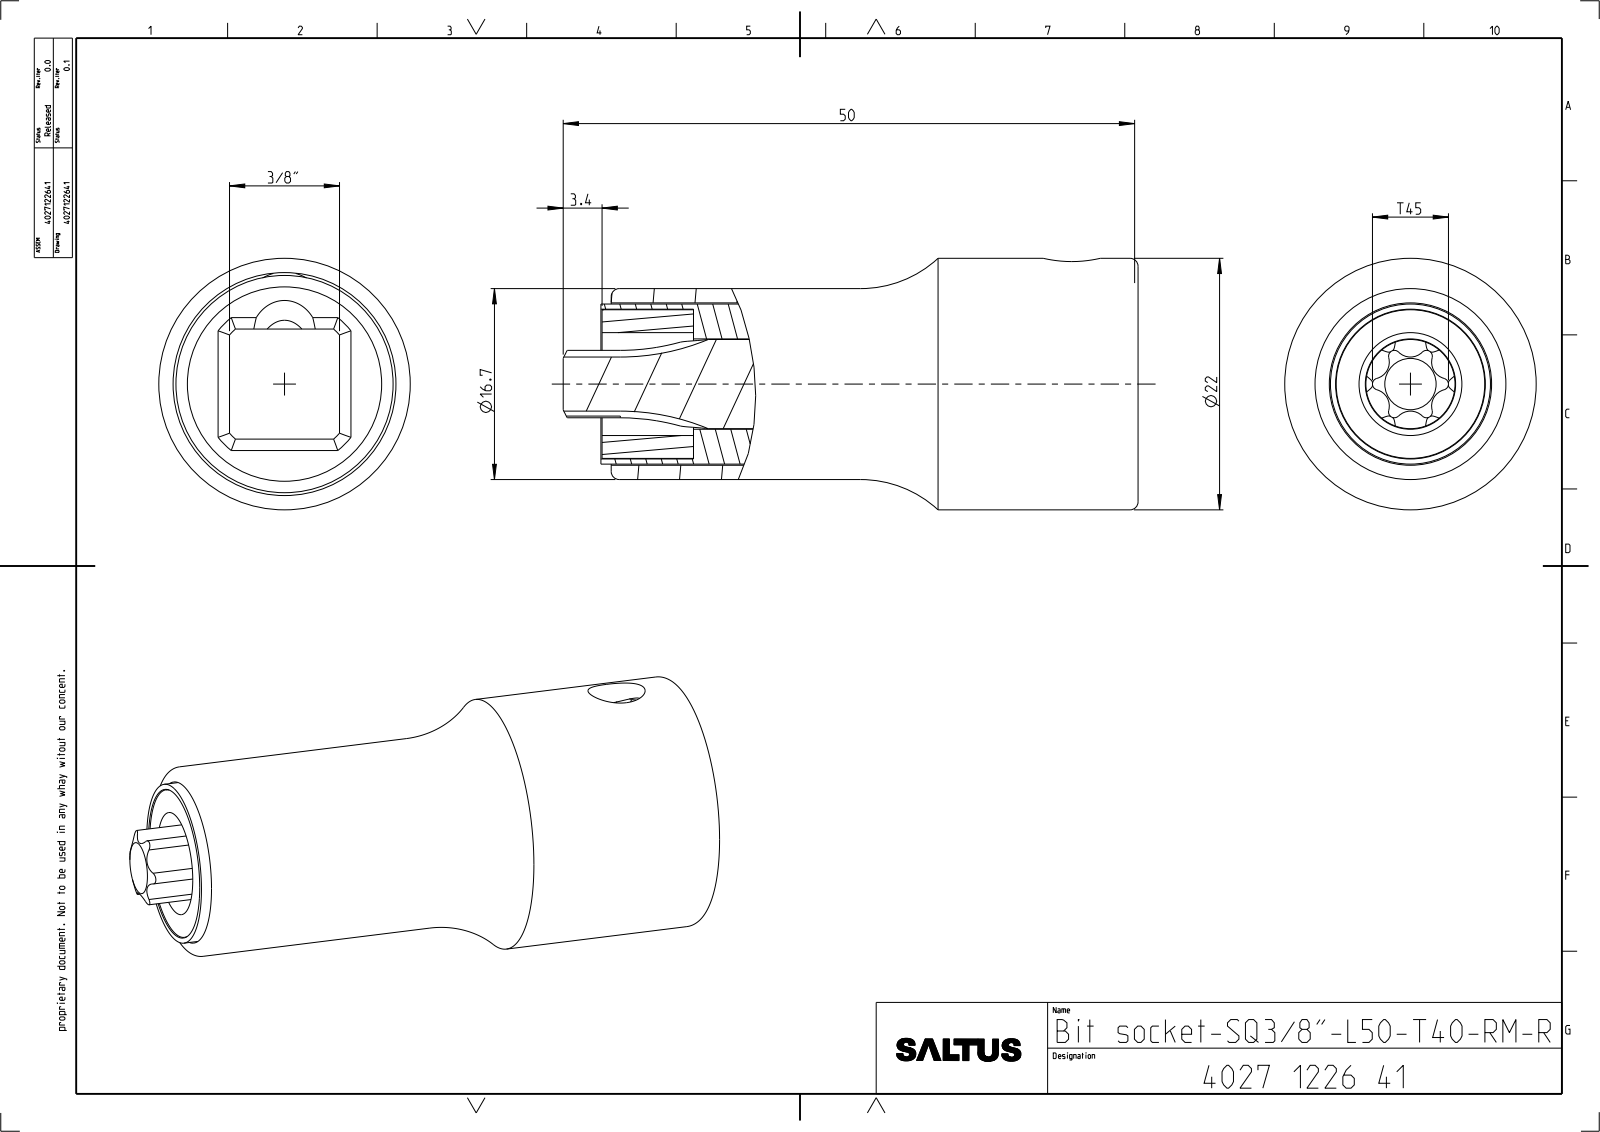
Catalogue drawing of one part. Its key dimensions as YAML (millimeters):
part_name: "4027905842; 4027901682; 4027907743; 4027904092_ASM (+2 more)"
step_written_by: "CREO PARAMETRIC BY PTC INC, 2022414 (CONFIG_CONTROL_DESIGN)"
units: millimeters
bodies: {solids: 4, faces: 124, planar: 20, cylindrical: 57, other: 47}
overall_size: [50.3, 22, 22]
volume: 9580
surface_area: 10039
round_holes:
  - {diameter: 5, count: 1}
  - {diameter: 7.9, count: 1}
  - {diameter: 9, count: 1}
  - {diameter: 13.1, count: 1}
  - {diameter: 14.2, count: 1}
  - {diameter: 19.5, count: 1}
round_bosses_or_shafts:
  - {diameter: 22, count: 1}
  - {diameter: 19, count: 1}
  - {diameter: 16.7, count: 1}
  - {diameter: 14, count: 1}
  - {diameter: 13, count: 1}
  - {diameter: 8, count: 1}
  - {diameter: 7.8, count: 1}
partial_cylinders:
  - {radius: 0.51, count: 6}
  - {radius: 1.47, count: 6}
  - {radius: 3, count: 1}
  - {radius: 3.33, count: 1}
  - {radius: 6.45, count: 1}
face_to_face_distances: [9.62, 27.1, 11.5, 38.6, 32.7, 21.2, 5.9, 46.6, 35.1, 13.9]
